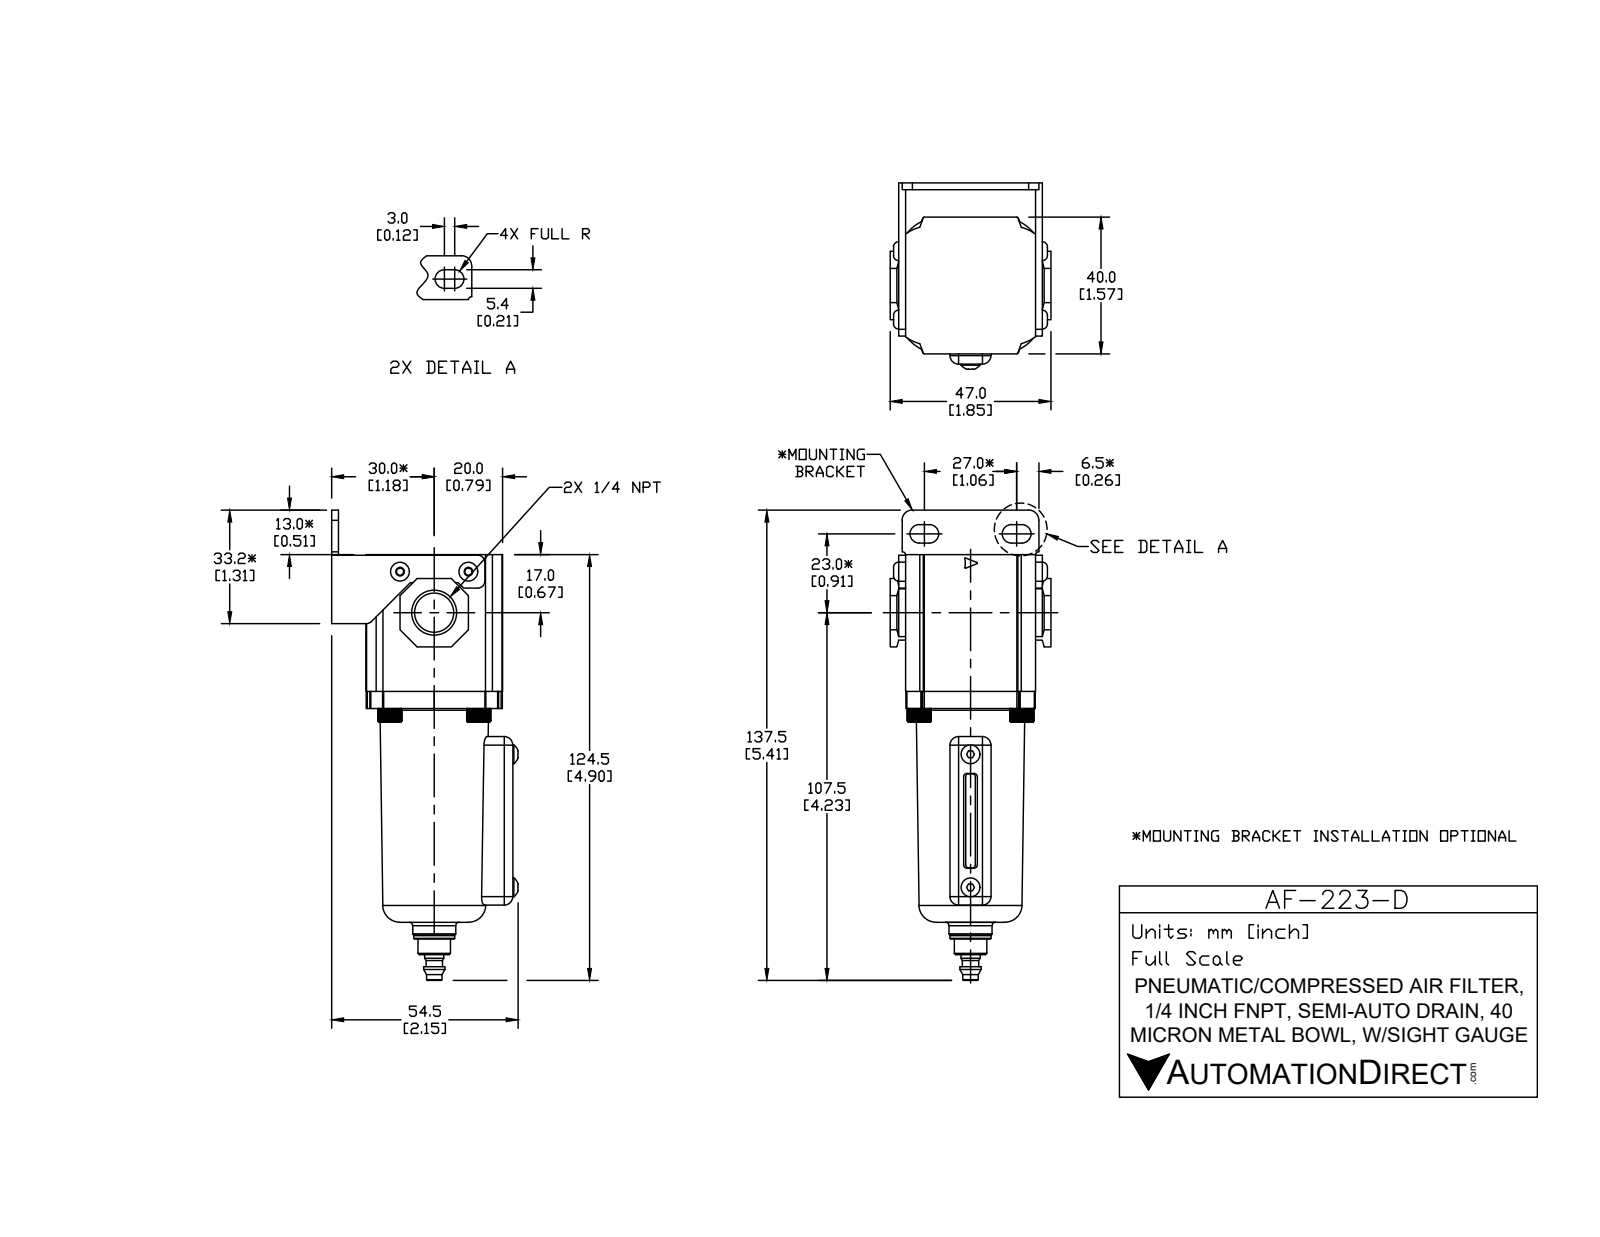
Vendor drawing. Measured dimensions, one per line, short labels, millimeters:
name: AF-223-D
written by: SolidWorks 2015 (CONFIG_CONTROL_DESIGN)
unit: mm
bodies: 9 solids, 385 faces (216 planar, 107 cylindrical, 62 other)
size: 137.5 × 55 × 47
volume: 118 759 mm³; area: 31 036 mm²
holes: 2× ⌀3.4, 1× ⌀3, 1× ⌀11.13
bosses: 4× ⌀7, 2× ⌀5.5, 1× ⌀12.6, 1× ⌀12, 1× ⌀9.53, 1× ⌀9.5, 1× ⌀6.2, 1× ⌀5.6
rounds: 12× R0.3, 8× R1.3, 8× R2.5, 5× R2, 4× R0.5, 4× R1, 4× R2.7, 4× R11.9
face distances: 40, 2, 38, 8, 10, 50, 48, 13, 15, 42
hole spacings: 15.62, 20
